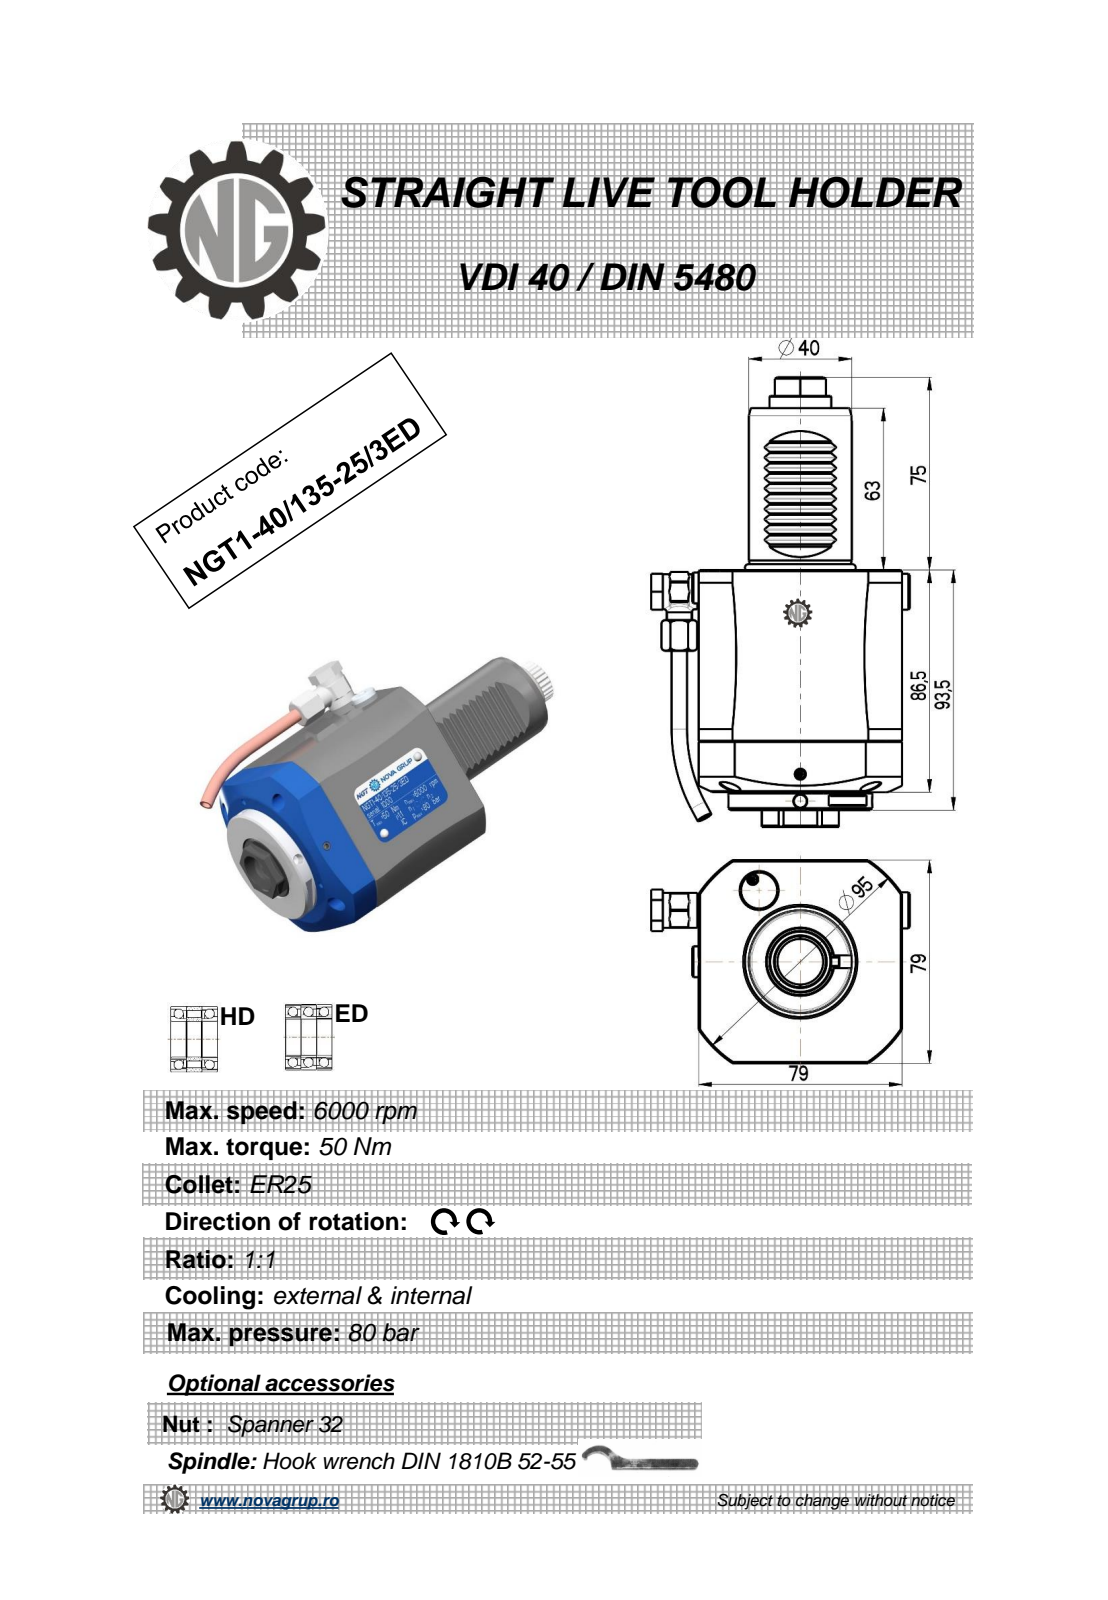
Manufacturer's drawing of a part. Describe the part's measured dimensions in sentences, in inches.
The part is named "NGT1_40_135_25_3HD". Its 3-D file was written by "PRO/ENGINEER BY PARAMETRIC TECHNOLOGY CORPORATION, 2010280 (CONFIG_CONTROL_DESIGN)". It is 2 solids with 502 faces: 154 planar, 204 cylindrical and 144 other. Overall it measures 6.89 by 3.953 by 3.11 inches. Its volume is 36.98 cubic inches and its surface area 83.68 square inches. Round holes: 3 of diameter 0.157, 2 of diameter 0.197, 1 of diameter 0.118, 1 of diameter 0.236, 1 of diameter 0.244, 1 of diameter 0.354, 1 of diameter 0.394, 1 of diameter 0.433, 1 of diameter 0.709, 1 of diameter 1.043. Round bosses or shafts: 1 of diameter 2.205, 1 of diameter 1.575, 1 of diameter 0.945, 1 of diameter 0.551, 1 of diameter 0.535, 1 of diameter 0.512, 1 of diameter 0.472, 1 of diameter 0.394. Partial cylindrical surfaces (rounded edges, fillets, slot ends): 48 of radius 0.082, 10 of radius 0.012, 6 of radius 0.016, 4 of radius 0.02, 1 of radius 0.303, 1 of radius 0.357, 1 of radius 0.391, 1 of radius 0.591. The main face-to-face distances are 3.11, 3.406, 0.276, 3.681, 0.111, 5.886, 6.161, 2.48, 0.334, 0.557. The hole center spacings are 0.016, 2.011, 2.026, 3.304.
